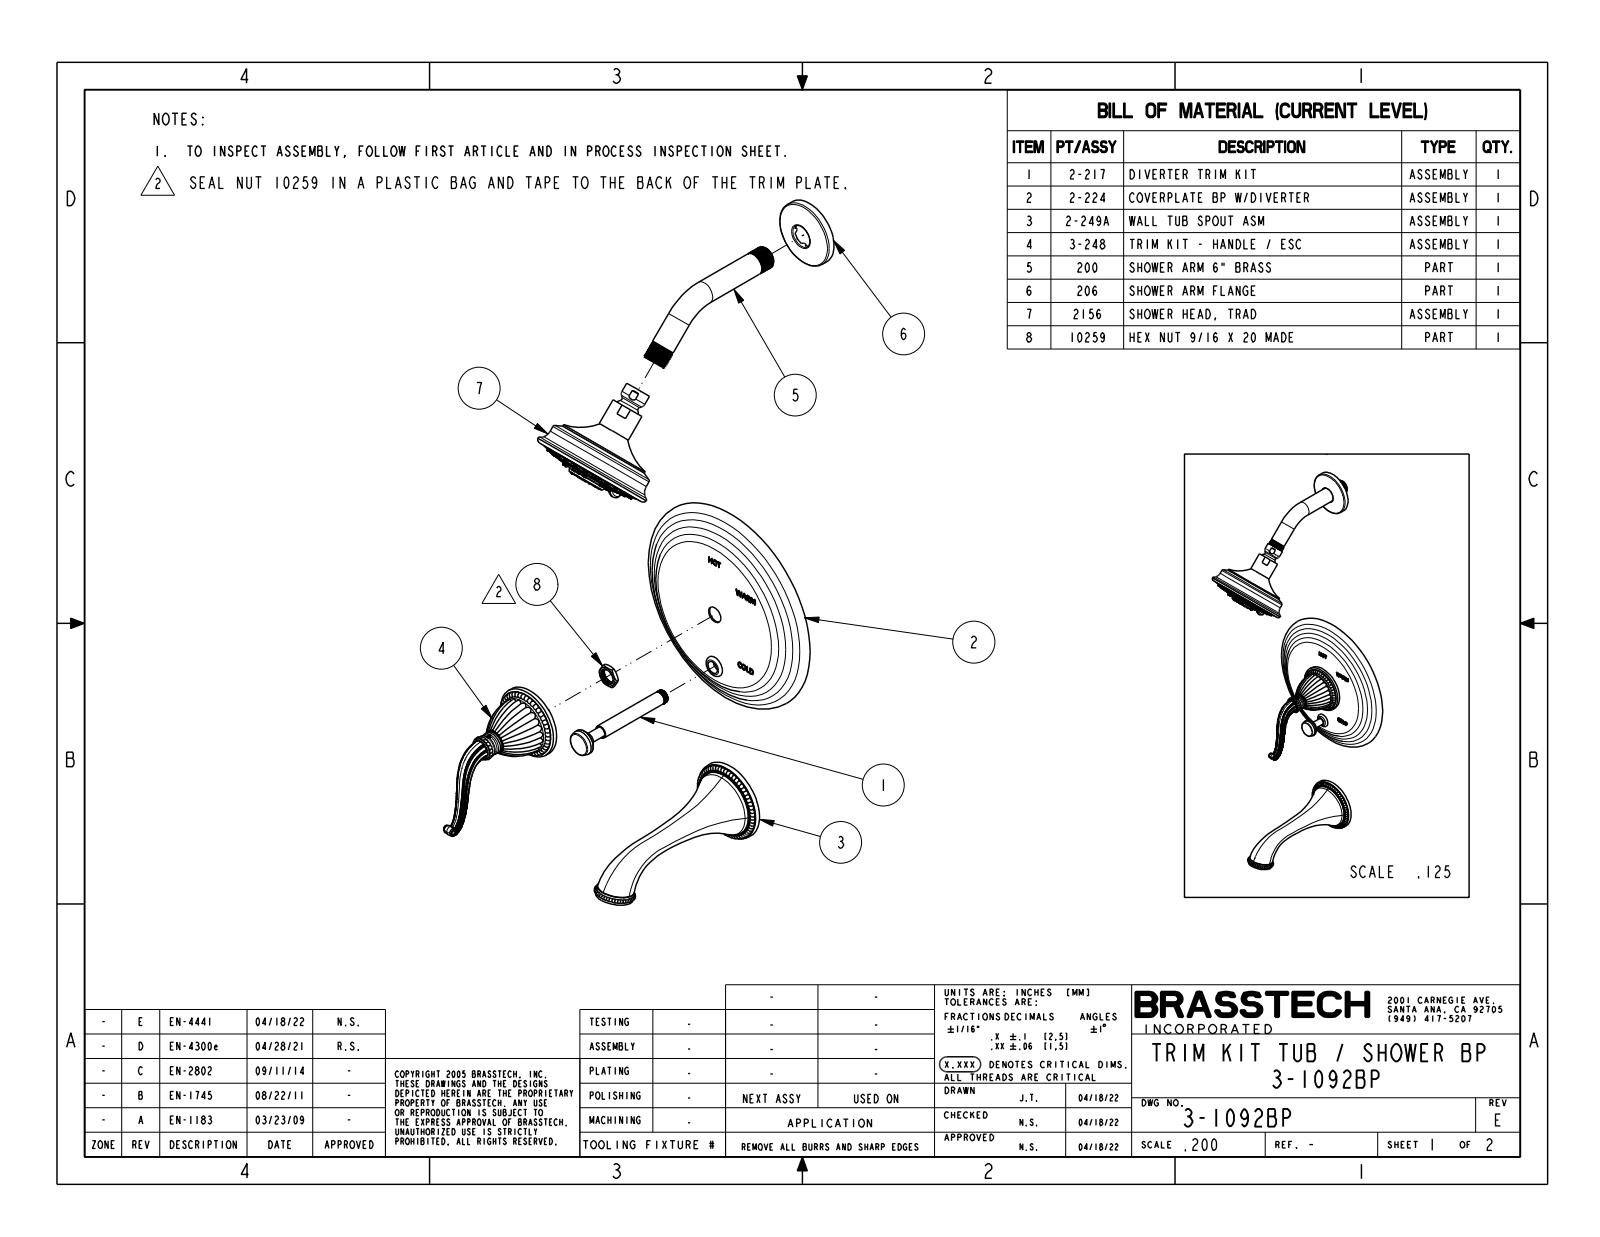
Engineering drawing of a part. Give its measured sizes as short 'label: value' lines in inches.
name: 3-1092BP
written by: CREO PARAMETRIC BY PTC INC, 2018400 (CONFIG_CONTROL_DESIGN)
unit: in
bodies: 8 solids, 4700 faces (653 planar, 1306 cylindrical, 2741 other)
size: 23.615 × 8.25 × 7.75
volume: 61.74 in³; area: 234.7 in²
holes: 189× ⌀0.04, 46× ⌀0.05, 22× ⌀0.045, 11× ⌀0.041, 8× ⌀0.059, 1× ⌀0.925
bosses: 39× ⌀0.142, 23× ⌀0.165, 3× ⌀0.05, 2× ⌀0.813, 1× ⌀3.81, 1× ⌀3.724, 1× ⌀3.24, 1× ⌀2.57
rounds: 8× R0.079, 2× R0.02, 1× R0.138, 1× R0.472, 1× R0.512, 1× R0.63
face distances: 0.754, 0.063, 0.118, 0.181, 2.006, 1.252, 0.29, 2.594, 1.84, 0.588
hole spacings: 0.443, 0.579, 1.069, 0.819, 0.369, 0.153, 0.304, 0.05
